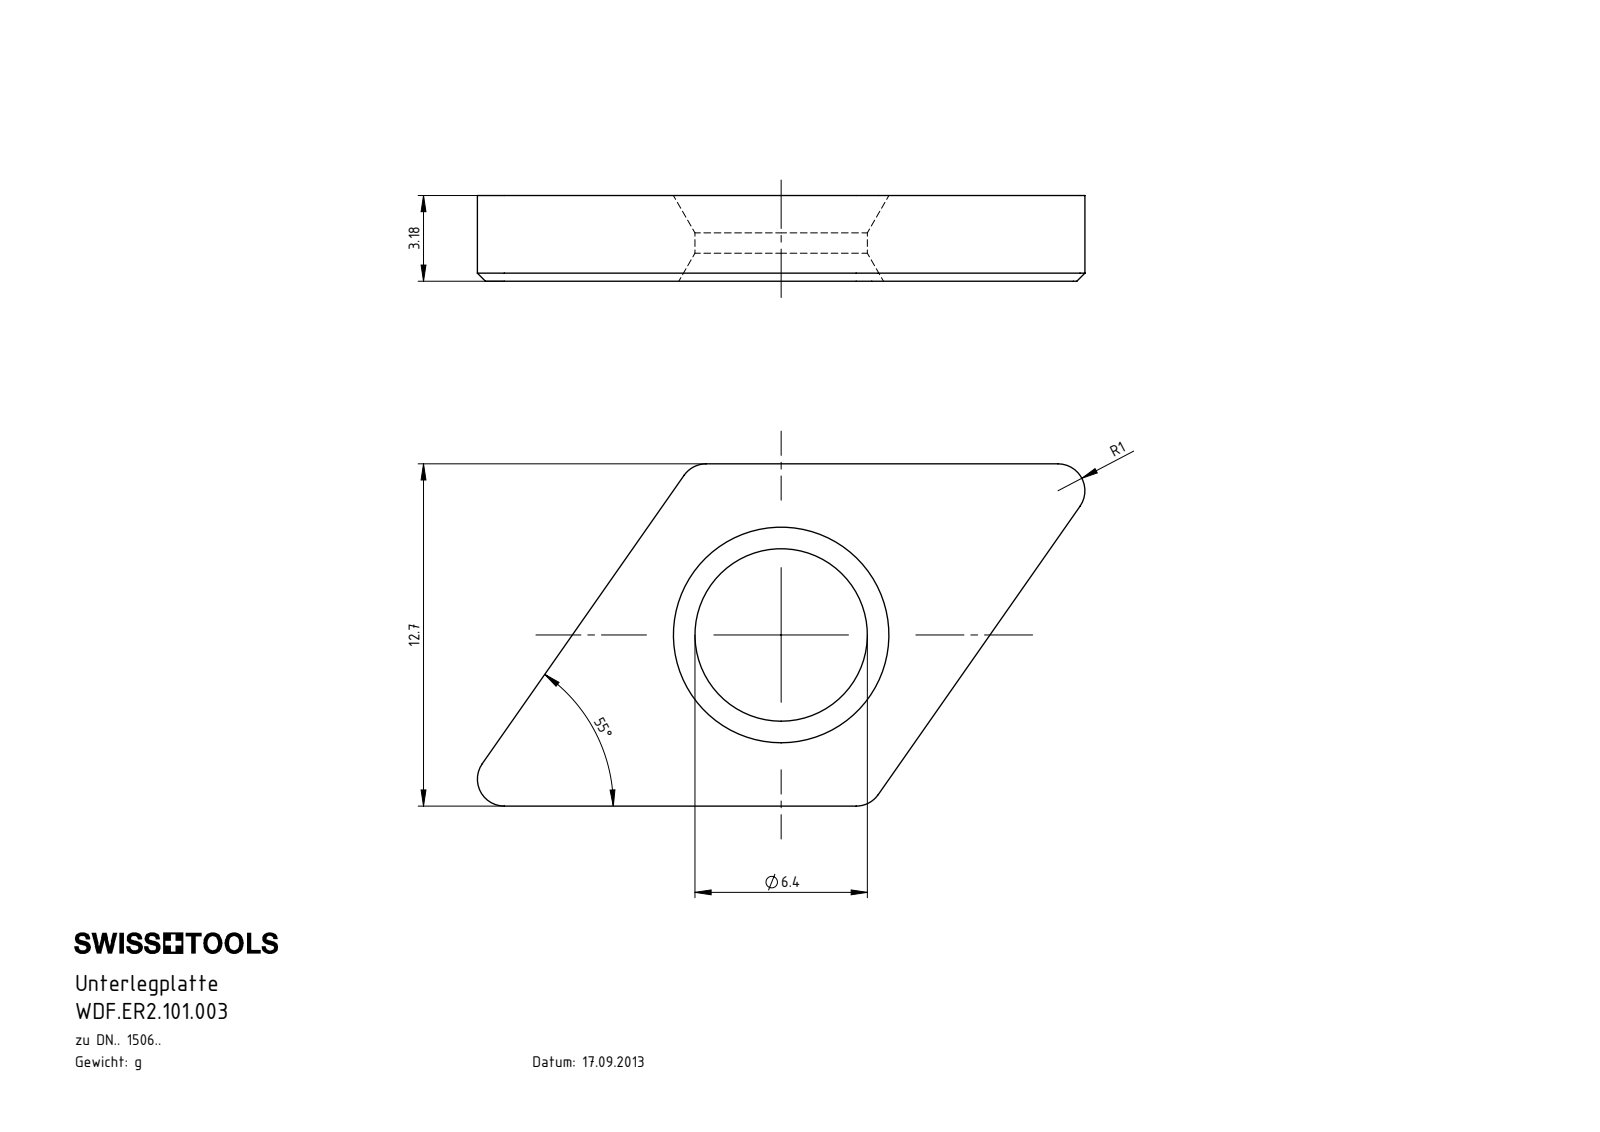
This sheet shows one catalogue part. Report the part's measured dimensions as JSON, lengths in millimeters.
{"part_name": "WDF.ER2.101.003", "step_written_by": "SolidWorks 2017 (AUTOMOTIVE_DESIGN)", "units": "millimeters", "bodies": {"solids": 1, "faces": 21, "planar": 10, "cylindrical": 5, "other": 6}, "overall_size": [22.55, 12.7, 3.18], "volume_mm3": 497, "surface_area_mm2": 548, "round_holes": [[6.4, 1]], "partial_cylinders_radius": [[1, 4]], "face_to_face_distances": [3.18, 12.7]}
